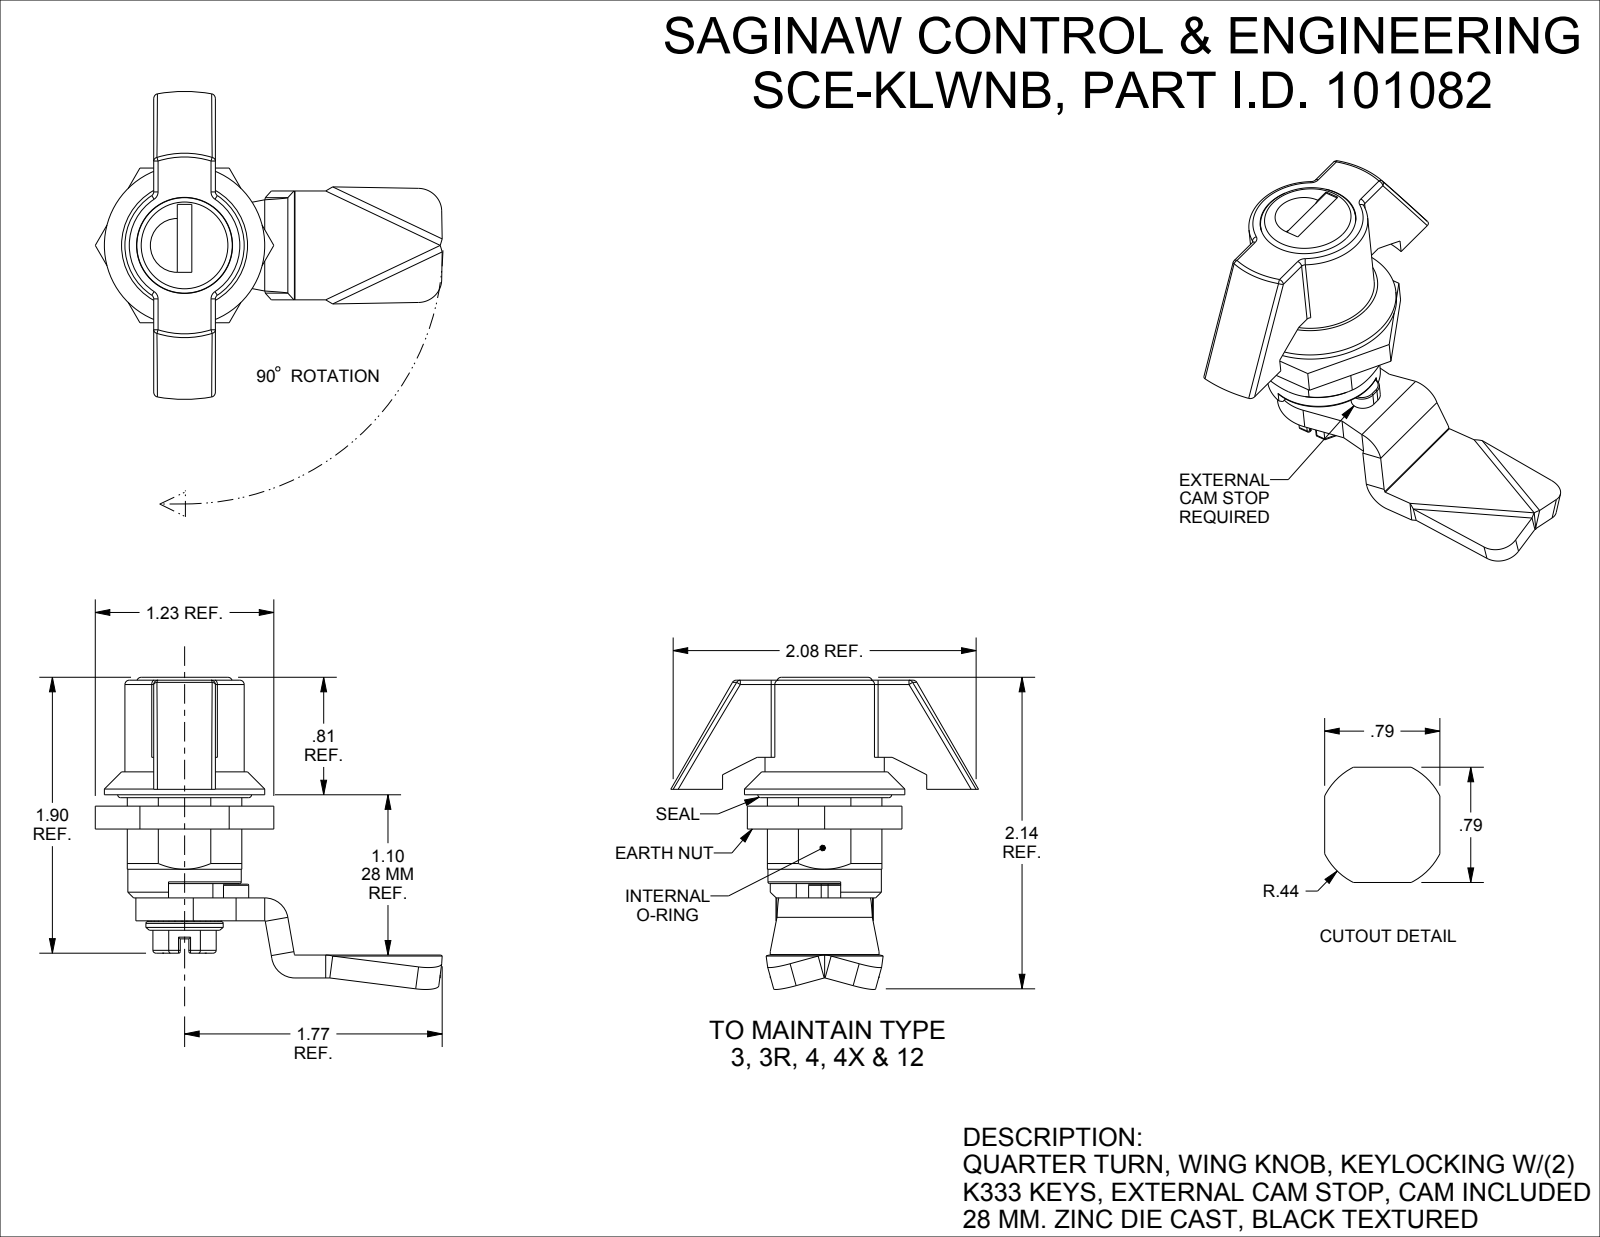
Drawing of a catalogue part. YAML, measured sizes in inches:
part_name: "SCE-KLWNB"
step_written_by: "SolidWorks 2021 (AUTOMOTIVE_DESIGN)"
units: inches
bodies: {solids: 7, faces: 332, planar: 140, cylindrical: 110, other: 82}
overall_size: [2.385, 2.145, 2.116]
volume: 1.389
surface_area: 21.75
round_holes:
  - {diameter: 0.197, count: 1}
  - {diameter: 0.315, count: 1}
  - {diameter: 0.394, count: 1}
  - {diameter: 0.634, count: 1}
  - {diameter: 0.66, count: 1}
  - {diameter: 0.799, count: 1}
round_bosses_or_shafts:
  - {diameter: 1.102, count: 1}
  - {diameter: 0.82, count: 1}
  - {diameter: 0.78, count: 1}
  - {diameter: 0.663, count: 1}
  - {diameter: 0.656, count: 1}
  - {diameter: 0.63, count: 1}
  - {diameter: 0.531, count: 1}
  - {diameter: 0.504, count: 1}
partial_cylinders:
  - {radius: 0.012, count: 30}
  - {radius: 0.02, count: 12}
  - {radius: 0.03, count: 6}
  - {radius: 0.157, count: 4}
  - {radius: 0.004, count: 2}
  - {radius: 0.008, count: 2}
  - {radius: 0.087, count: 2}
  - {radius: 0.161, count: 2}
face_to_face_distances: [0.157, 0.235, 1.023, 1.259, 0.631, 0.393, 0.866, 0.433, 0.787, 0.55]
